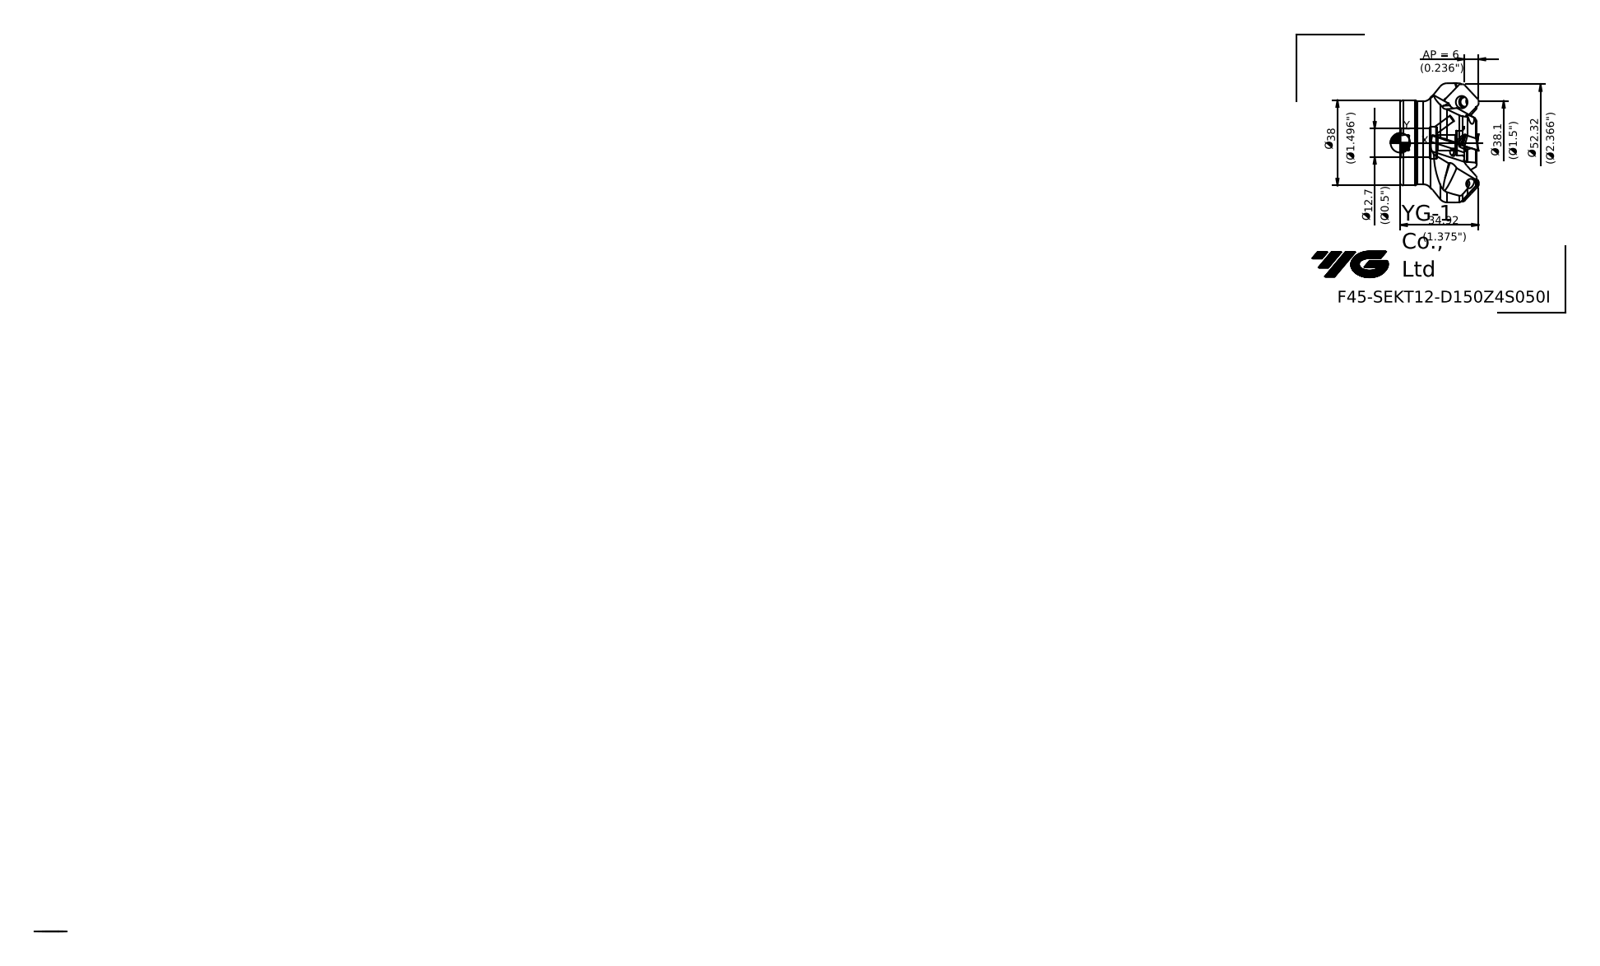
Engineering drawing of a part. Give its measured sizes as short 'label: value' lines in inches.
name: 1022435806C4225v
written by: SIEMENS PLM Software NX 10.0 (AP203_CONFIGURATION_CONTROLLED_3D_DESIGN_OF_MECHANICAL_PARTS_AND_ASSEMBLIES_MIM_LF)
unit: in
bodies: 1 solid, 74 faces (16 planar, 11 cylindrical, 47 other)
size: 2.094 × 2.094 × 1.375
volume: 2.842 in³; area: 22.28 in²
holes: 1× ⌀0.276, 1× ⌀0.433, 1× ⌀0.5, 1× ⌀0.563
bosses: 1× ⌀2.094, 1× ⌀1.496, 1× ⌀1.457
rounds: 2× R0.016
face distances: 1.117, 0.957, 0.16, 0.478, 0.48, 0.64, 0.266, 0.133, 0.344, 0.824
